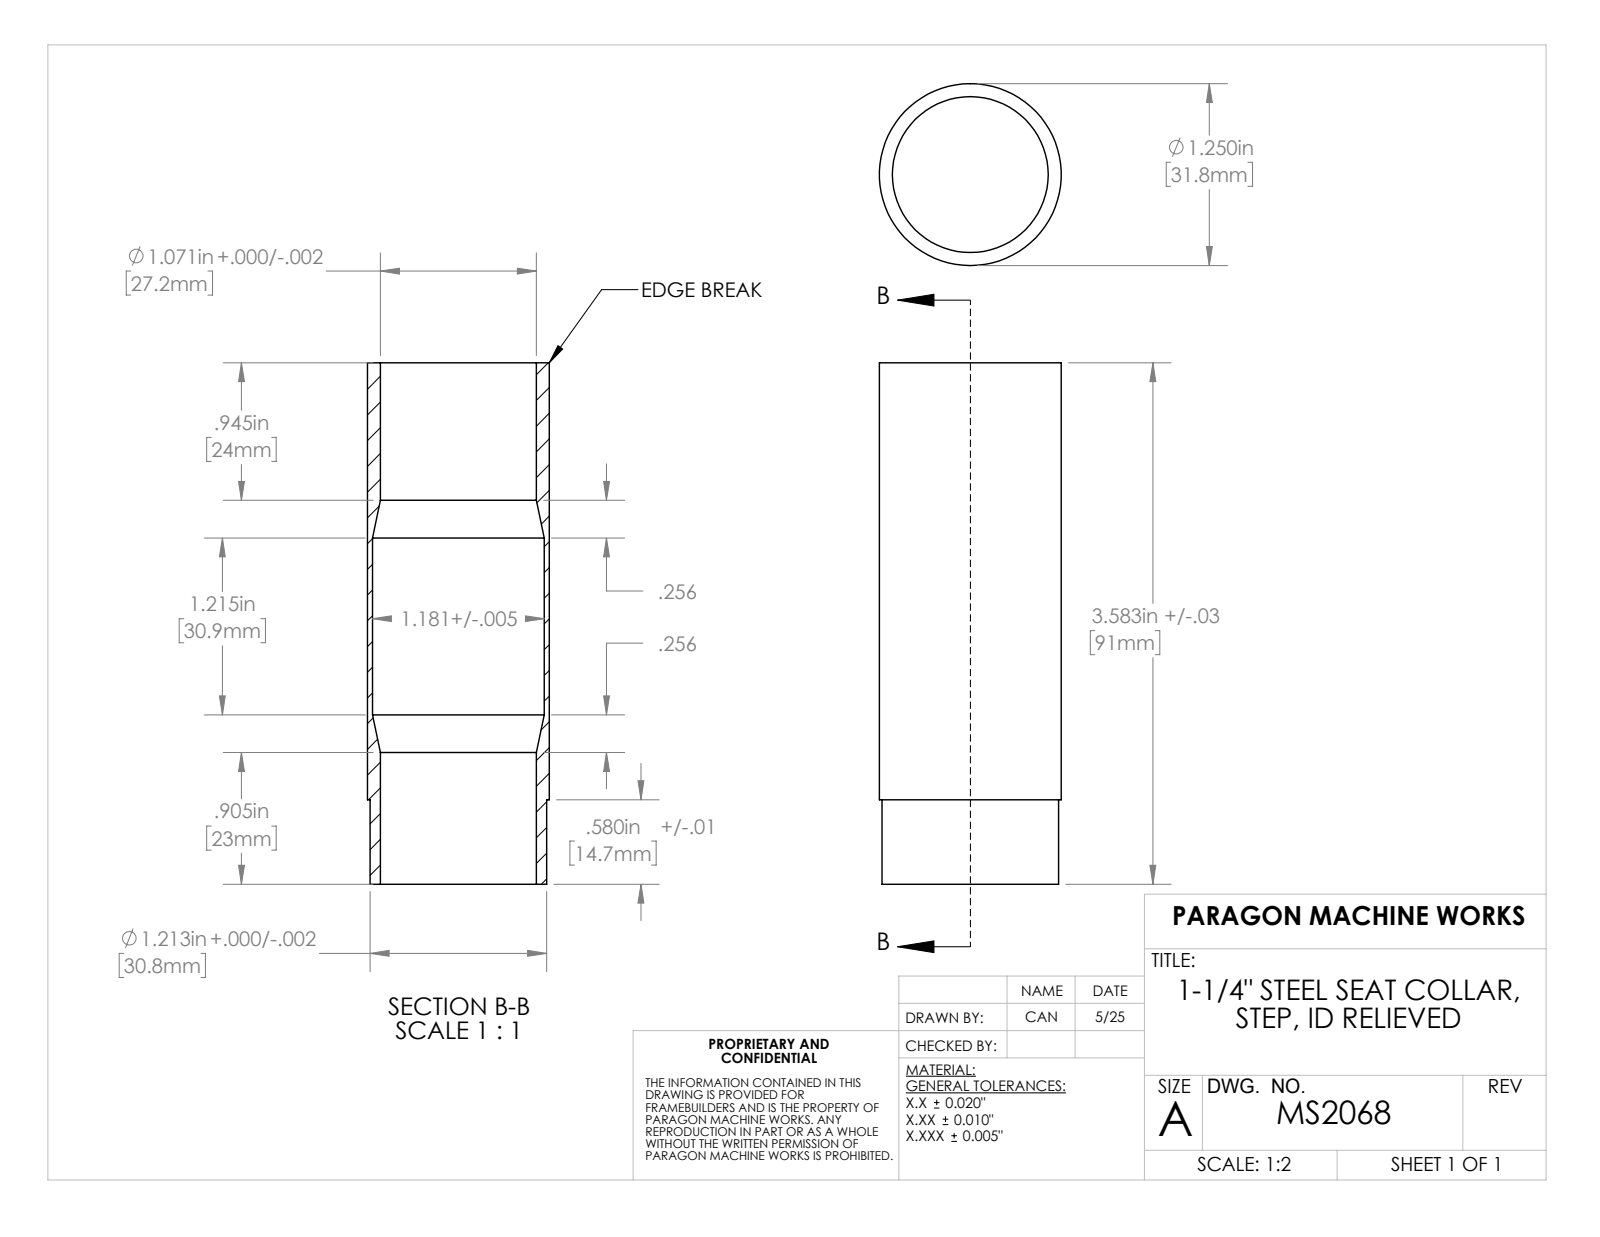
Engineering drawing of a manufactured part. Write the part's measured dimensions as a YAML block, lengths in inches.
part_name: "MS2068"
step_written_by: "SolidWorks 2023 (AUTOMOTIVE_DESIGN)"
units: inches
bodies: {solids: 1, faces: 17, planar: 3, cylindrical: 10, other: 4}
overall_size: [3.583, 1.25, 1.25]
volume: 0.842
surface_area: 27.26
round_holes:
  - {diameter: 1.071, count: 1}
  - {diameter: 1.181, count: 1}
round_bosses_or_shafts:
  - {diameter: 1.25, count: 1}
  - {diameter: 1.213, count: 1}
face_to_face_distances: [3.583, 0.58, 3.003]
